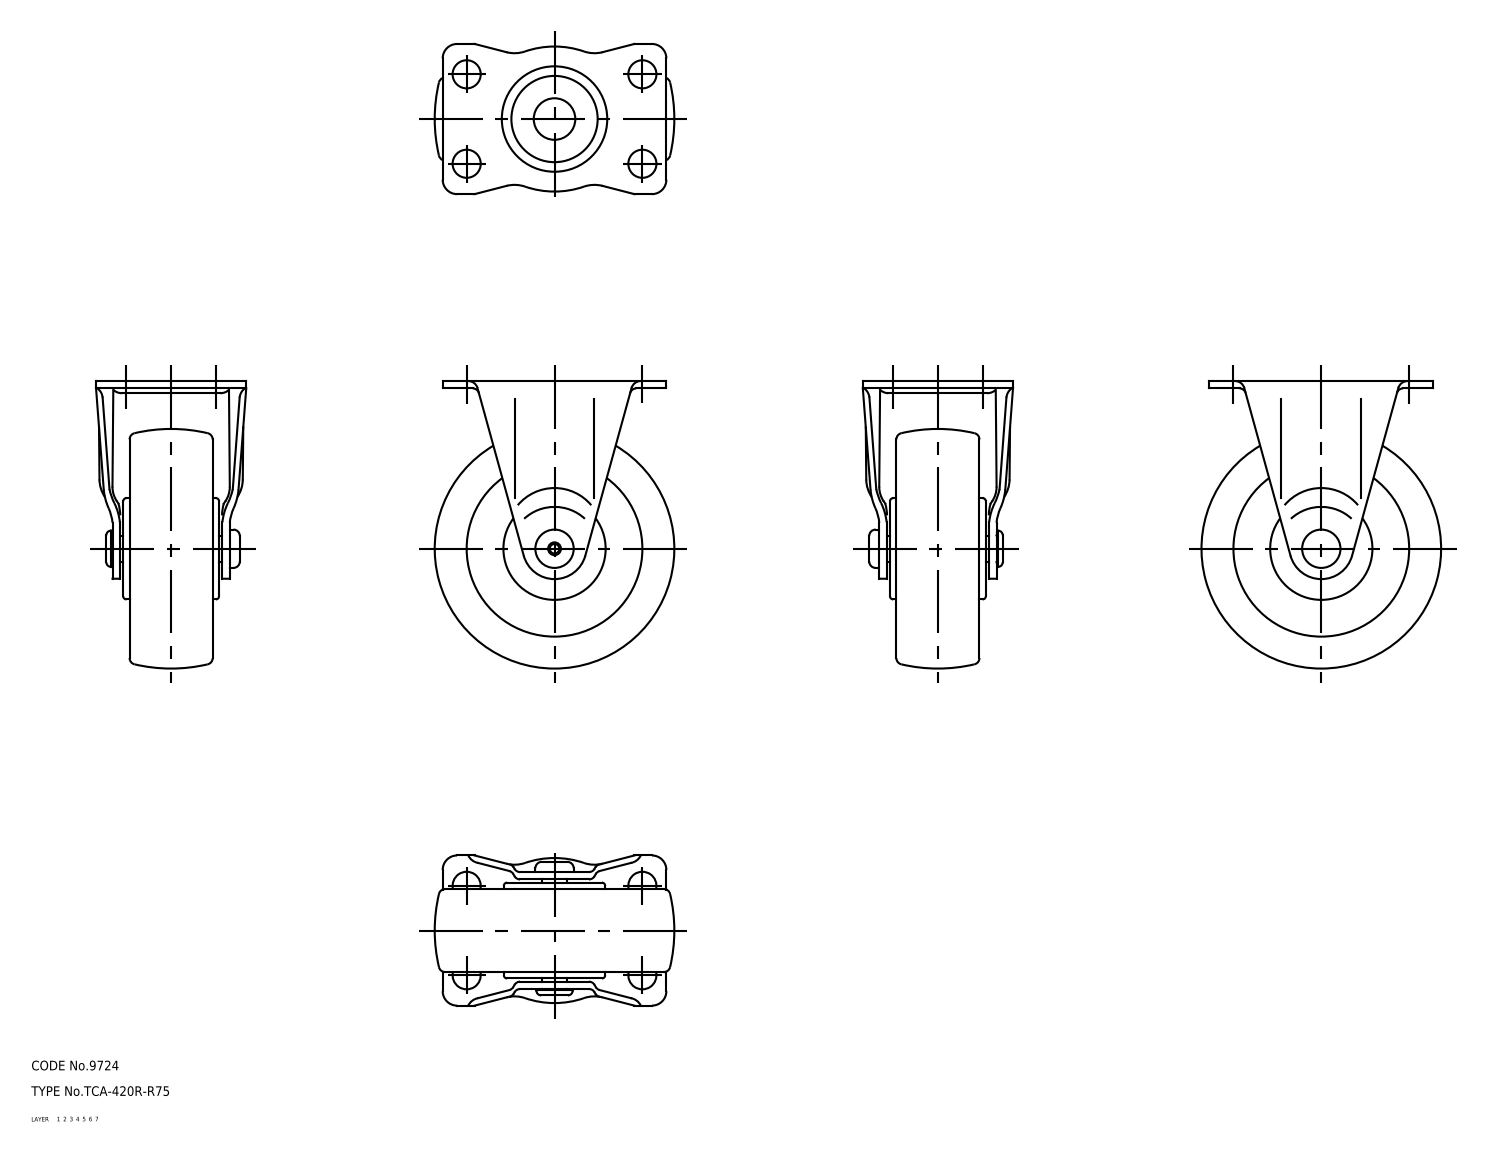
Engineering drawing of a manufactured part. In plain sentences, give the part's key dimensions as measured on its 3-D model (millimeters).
The part is named "wheel; axle; No_420_R_R75_6_13671_36". Its 3-D file was written by "CADfix (AUTOMOTIVE_DESIGN)". It is 3 solids with 182 faces: 0 planar, 0 cylindrical and 182 other. Overall it measures 90 by 75 by 47 millimeters. Its volume is 126 981 cubic millimeters and its surface area 31 181 square millimeters.
